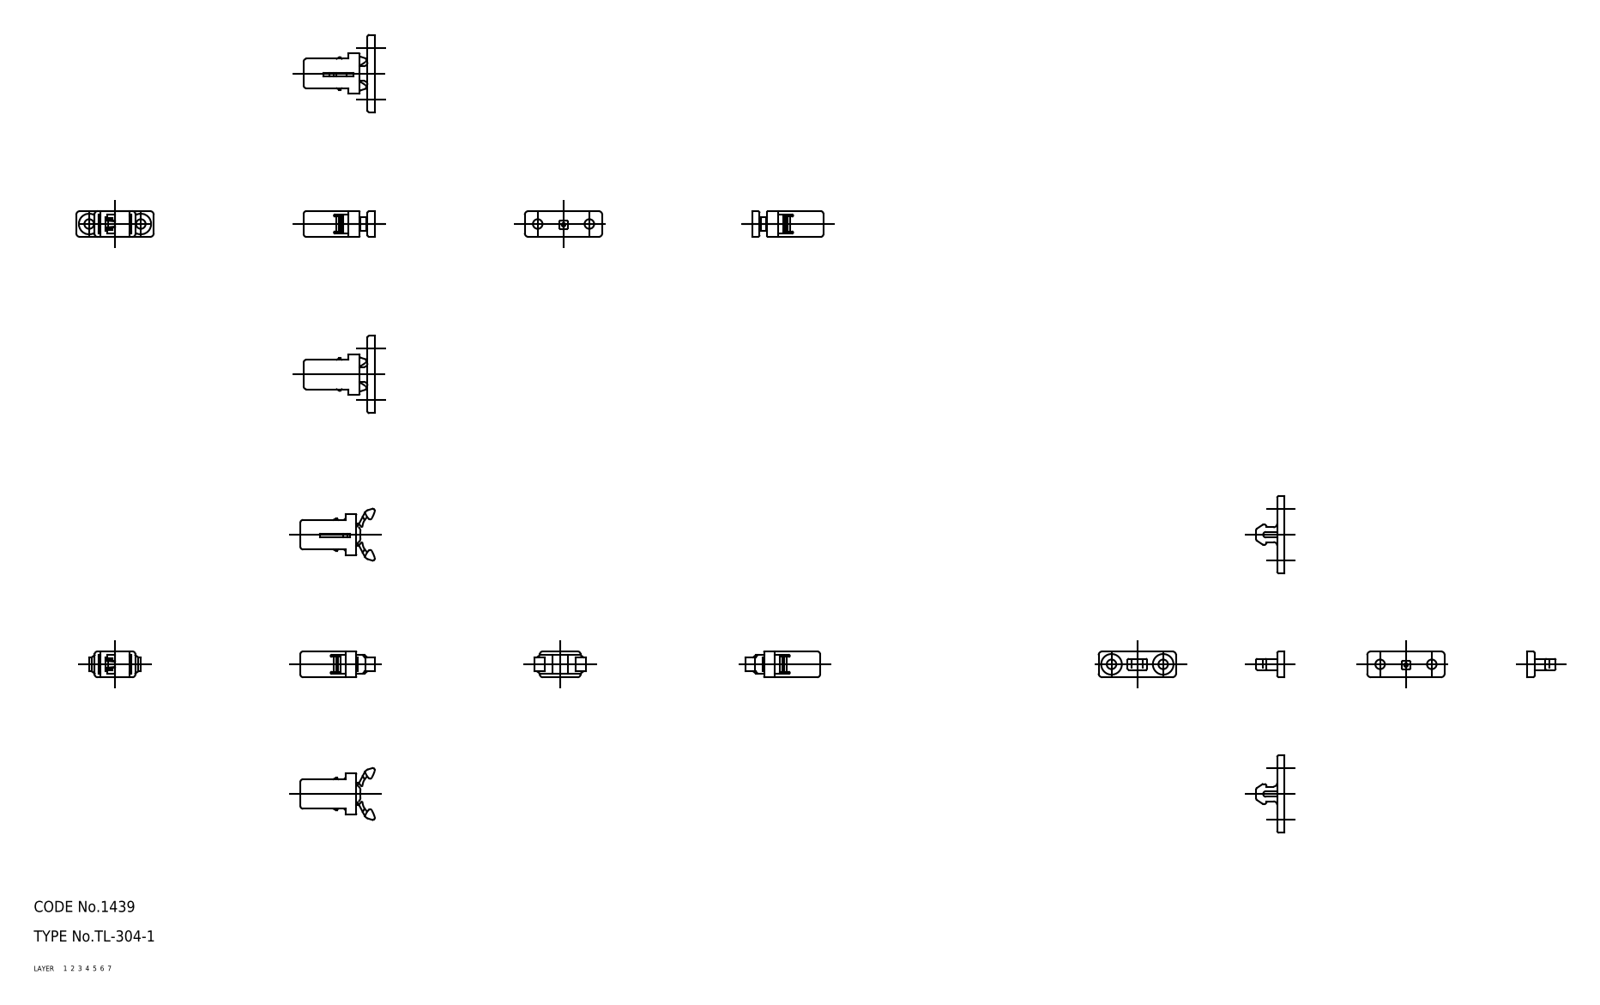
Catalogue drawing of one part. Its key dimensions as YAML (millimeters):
part_name: "keeper; housing; arm; TL_304_1_7919_36"
step_written_by: "CADfix (AUTOMOTIVE_DESIGN)"
units: millimeters
bodies: {solids: 3, faces: 242, planar: 0, cylindrical: 0, other: 242}
overall_size: [64.17, 21, 7]
volume: 1045
surface_area: 1845
